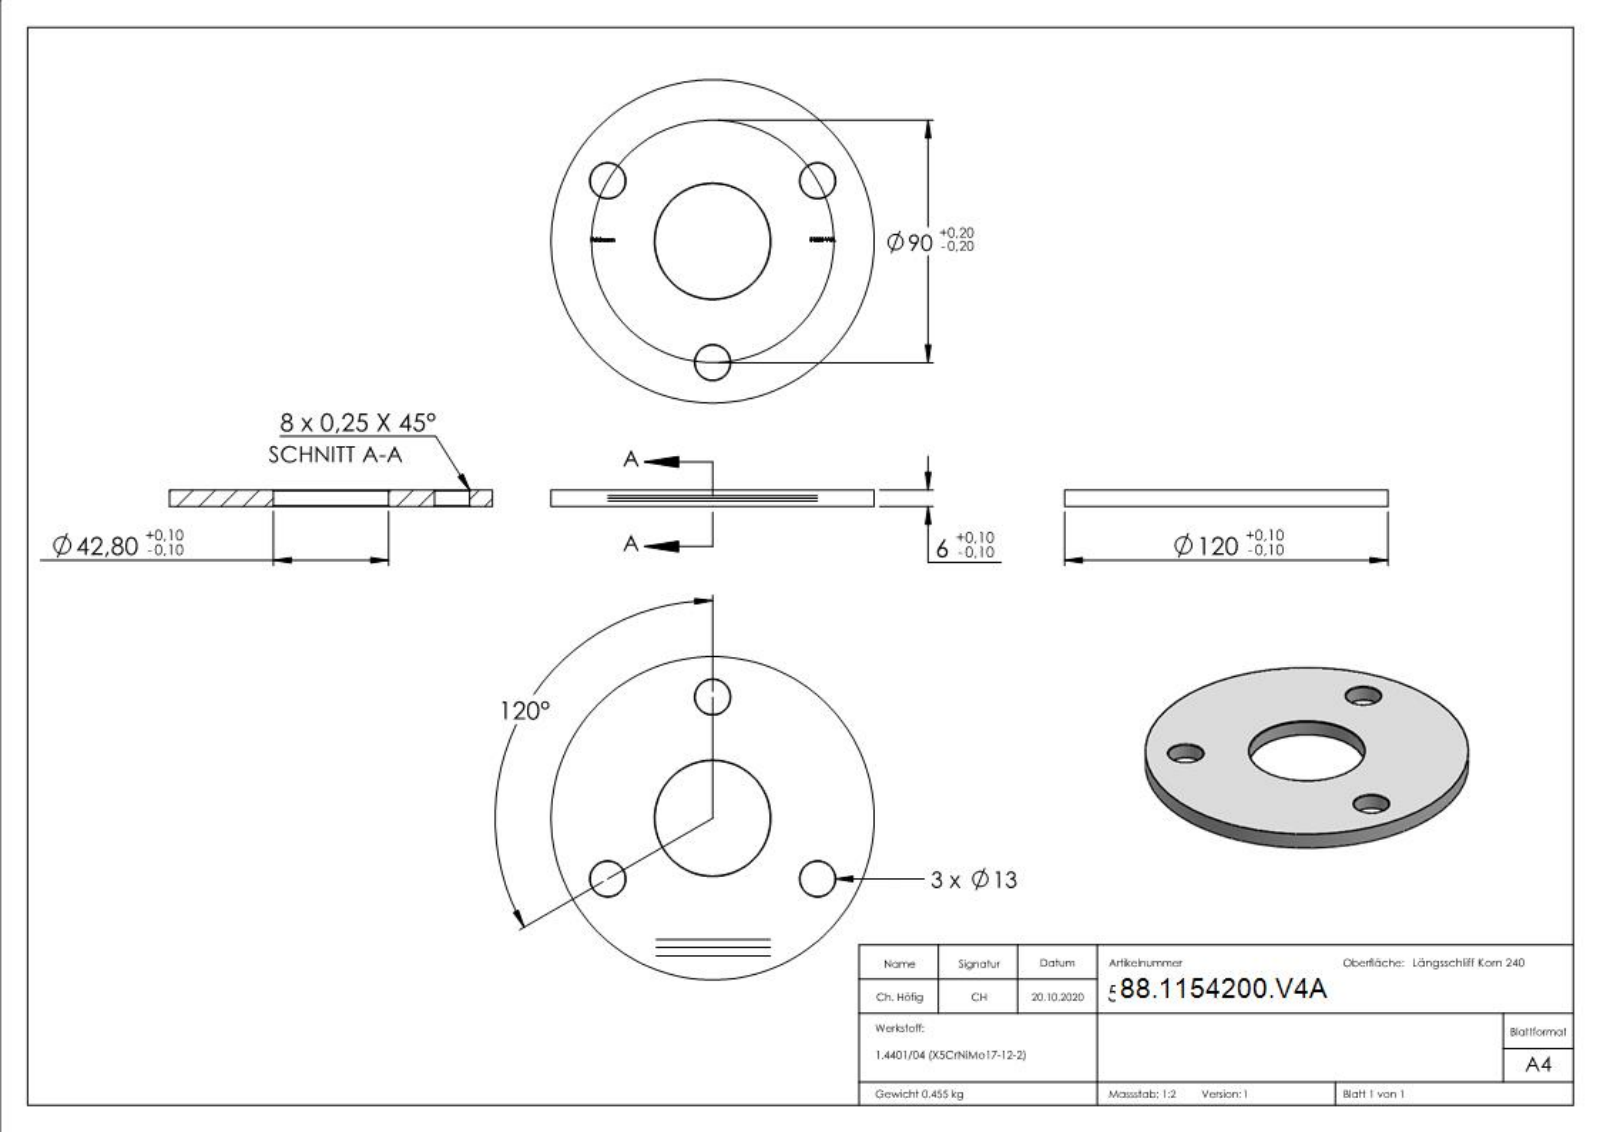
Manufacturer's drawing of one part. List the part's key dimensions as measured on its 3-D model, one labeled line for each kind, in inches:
Part name (STEP PRODUCT): 54200-V4A
STEP written by: SolidWorks 2018 (CONFIG_CONTROL_DESIGN)
Units: inches
Bodies: 1 solid, 247 faces (141 planar, 10 cylindrical, 96 other)
Overall size (bounding box): 4.724 × 4.724 × 0.236
Volume: 3.467 in³ · Surface area: 35.16 in²
Round holes (diameter × count): ⌀0.512 ×3, ⌀1.685 ×1
Round bosses / shafts (diameter × count): ⌀4.724 ×1
Main face-to-face distances: 0.236, 0.232, 0.015, 0.117, 0.017, 0.035, 0.08, 3.185, 3.42, 0.235
Hole centre spacings: 1.772, 3.069
